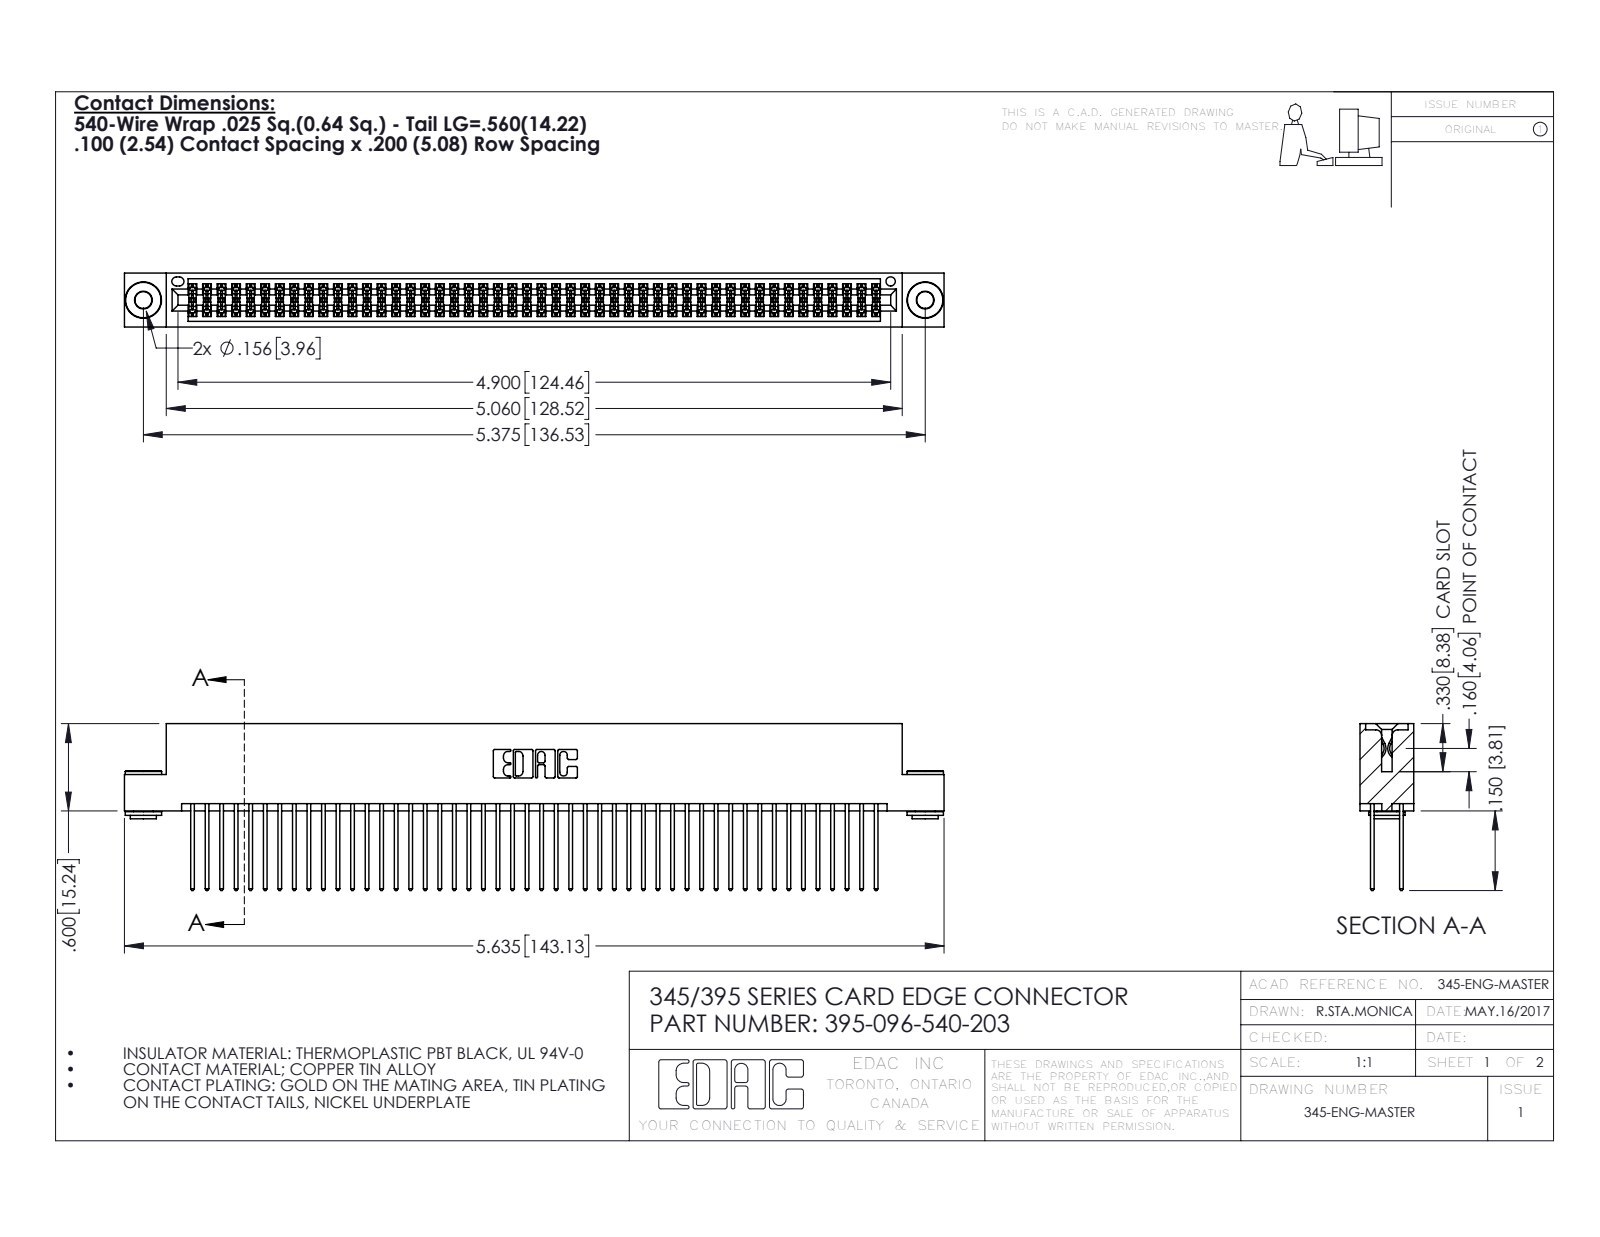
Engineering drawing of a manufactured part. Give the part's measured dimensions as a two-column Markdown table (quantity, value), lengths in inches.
| quantity | value |
| --- | --- |
| part name | 345-292-001_345-293-140; 345-250-002_345-250-002-102; 395-096-540-203; 345 Part_Flush Mounting Lugs - 0.156 Dia-TH |
| STEP written by | SolidWorks 2016 (CONFIG_CONTROL_DESIGN) |
| units | inches |
| bodies | 99 solids, 4964 faces (3258 planar, 1698 cylindrical, 8 other) |
| overall size | 5.635 × 1.147 × 0.37 |
| volume | 0.875 in³ |
| surface area | 35.98 in² |
| round holes (diameter × count) | 0.116 × 2, 0.156 × 2, 0.064 × 1 |
| round bosses / shafts (diameter × count) | 0.25 × 2, 0.18 × 2, 0.136 × 2 |
| partial cylindrical surfaces (radius × count) | 0.006 × 144, 0.01 × 96, 0.01 × 22, 0.007 × 6, 0.031 × 6, 0.026 × 3, 0.014 × 2, 0.019 × 2 |
| main face-to-face distances | 0.072, 0.298, 0.2, 0.025, 0.098, 0.272, 0.225, 0.37, 0.175, 0.149 |
| hole center spacings | 0.27, 5.139, 5.375 |
